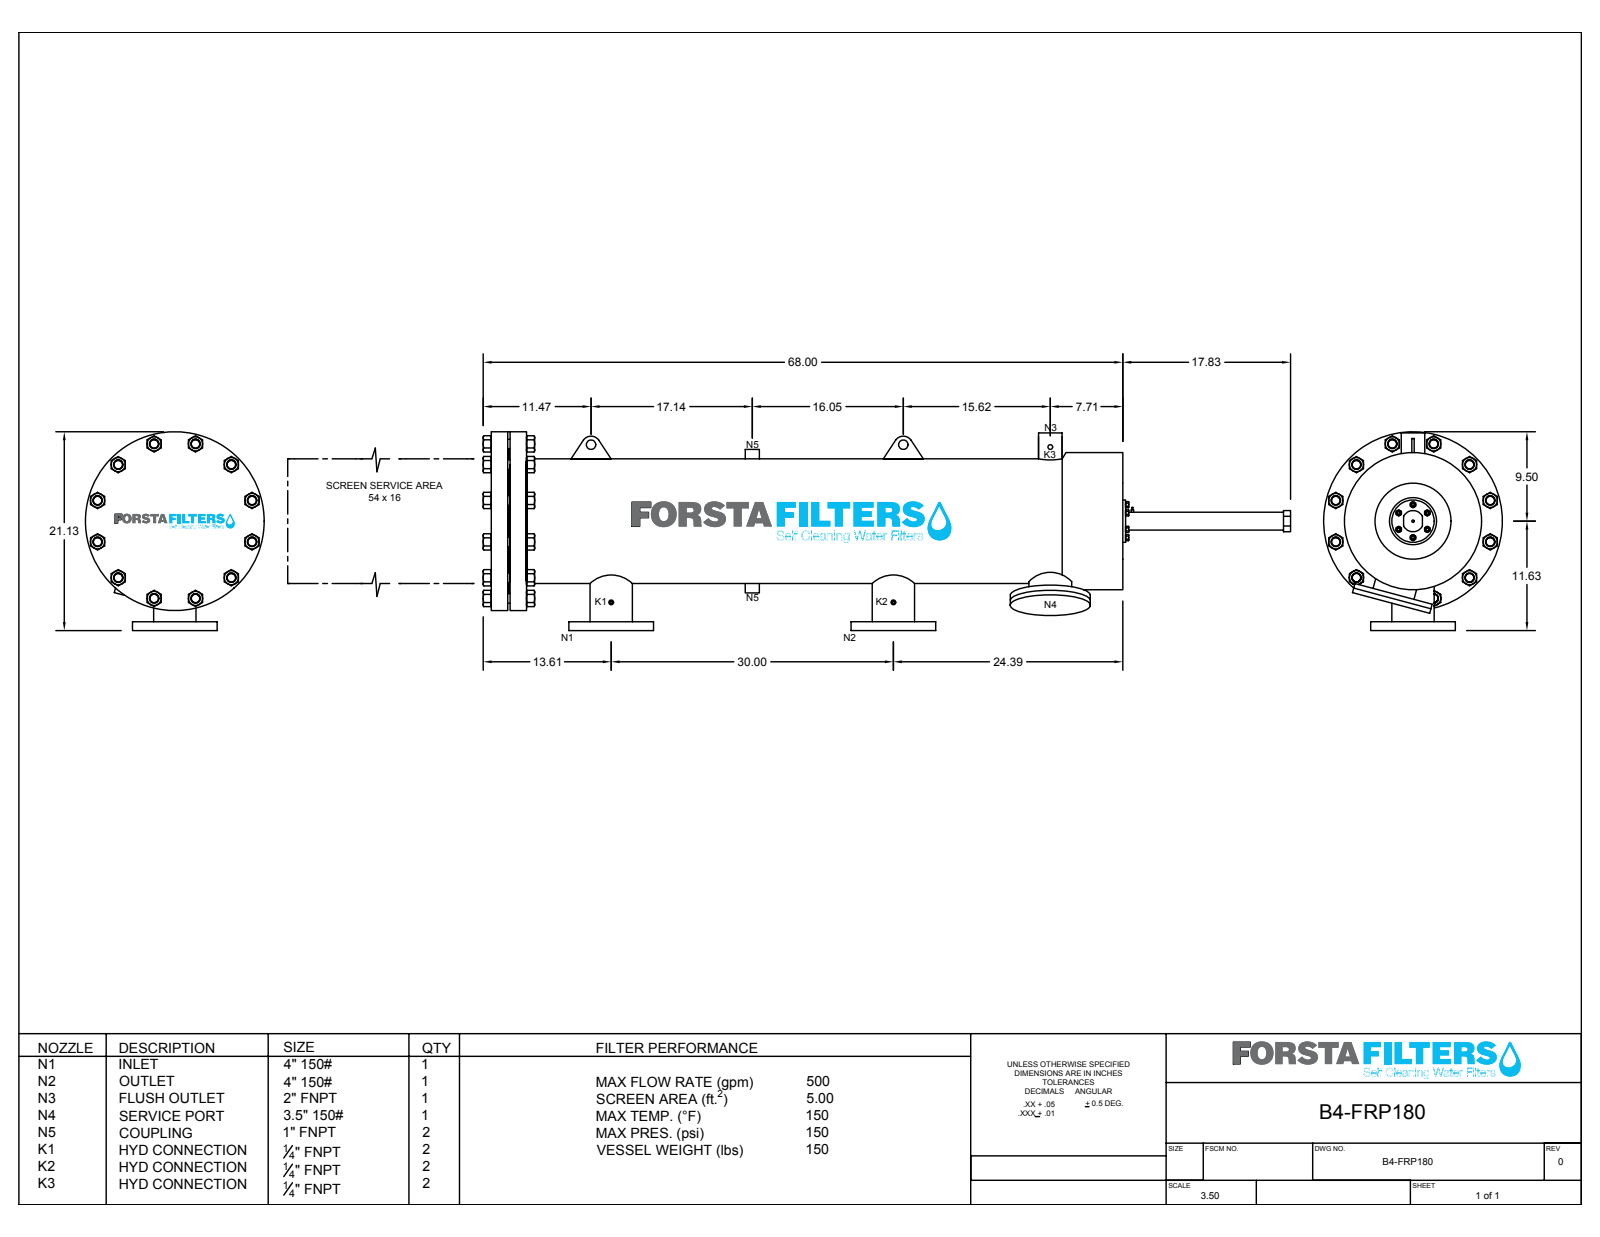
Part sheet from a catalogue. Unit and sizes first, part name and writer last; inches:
Units: inches
Overall size (bounding box): 82.235 × 21.13 × 19
Round holes (diameter × count): ⌀0.75 ×32, ⌀1 ×15, ⌀0.375 ×5, ⌀4 ×4, ⌀0.246 ×2, ⌀0.25 ×2, ⌀0.375 ×1, ⌀1.51 ×1, ⌀2 ×1, ⌀12.856 ×1, ⌀14.187 ×1
Round bosses / shafts (diameter × count): ⌀9 ×4, ⌀4.394 ×4, ⌀0.64 ×2, ⌀19 ×1, ⌀14.581 ×1, ⌀4.504 ×1, ⌀2.394 ×1, ⌀1.904 ×1
Partial cylindrical surfaces — rounded edges, fillets, slot ends (radius × count): R1 ×2, R1.125 ×1
Main face-to-face distances: 2, 1.75, 0.25, 0.5, 63.711, 61.961, 61.711, 3.75, 59.961, 0.197
Hole centre spacings: 2.87, 3.75, 5.303, 6.929, 7.5, 8.5, 1.752, 8.222
Volume: 1 622 in³ · Surface area: 8 587 in²
Bodies: 31 solids, 641 faces (305 planar, 326 cylindrical, 10 other)
Part name (STEP PRODUCT): B4-FRP-180
STEP written by: SolidWorks 2018 (CONFIG_CONTROL_DESIGN)
